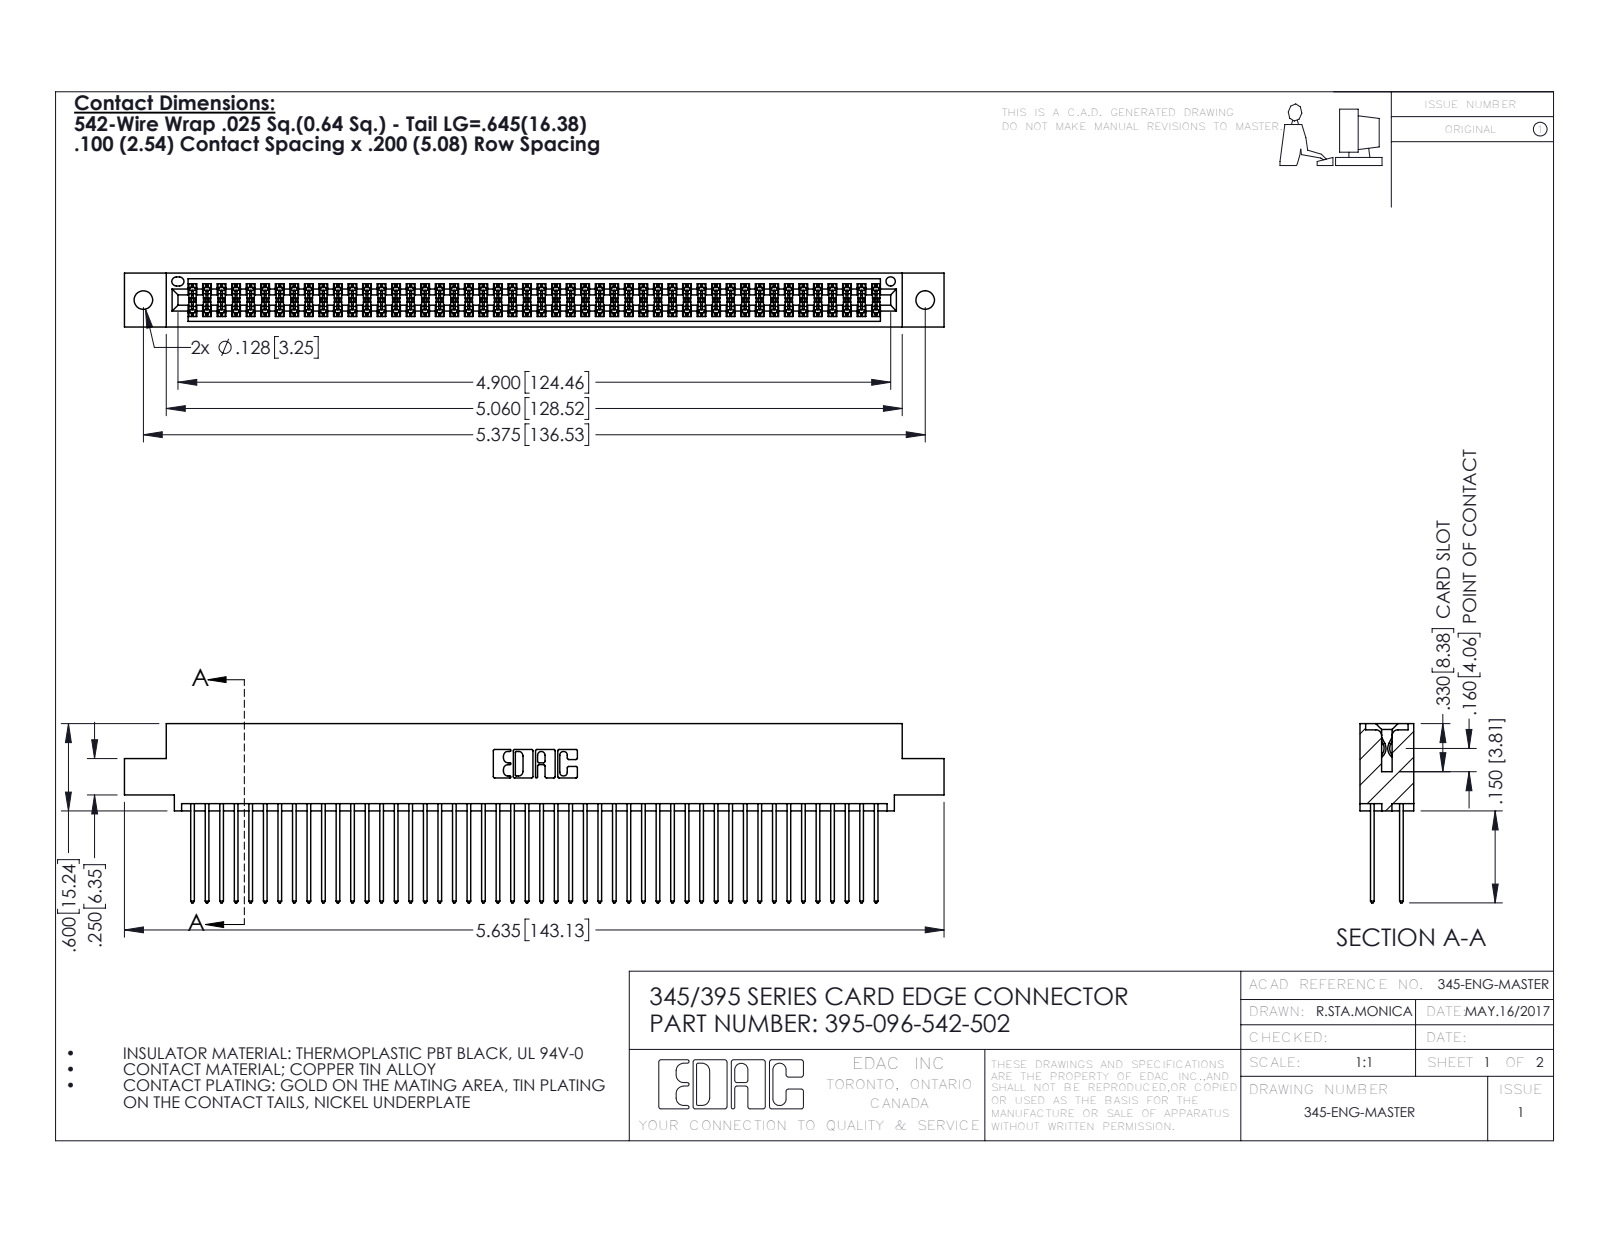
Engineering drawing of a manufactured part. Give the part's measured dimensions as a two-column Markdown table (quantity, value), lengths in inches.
| quantity | value |
| --- | --- |
| part name | 345-292-001_345-293-142; 345 Part_0.110 Offset - 0.128 Dia; 395-096-542-502 |
| STEP written by | SolidWorks 2016 (CONFIG_CONTROL_DESIGN) |
| units | inches |
| bodies | 97 solids, 4930 faces (3252 planar, 1678 cylindrical, 0 other) |
| overall size | 5.635 × 1.232 × 0.37 |
| volume | 0.872 in³ |
| surface area | 35.9 in² |
| round holes (diameter × count) | 0.128 × 2, 0.064 × 1 |
| partial cylindrical surfaces (radius × count) | 0.006 × 144, 0.01 × 96, 0.01 × 22, 0.007 × 6, 0.031 × 6, 0.026 × 3, 0.014 × 2, 0.019 × 2 |
| main face-to-face distances | 0.298, 0.072, 0.2, 0.098, 0.272, 0.025, 0.225, 0.37, 0.175, 0.149 |
| hole center spacings | 0.27, 5.139, 5.375 |
